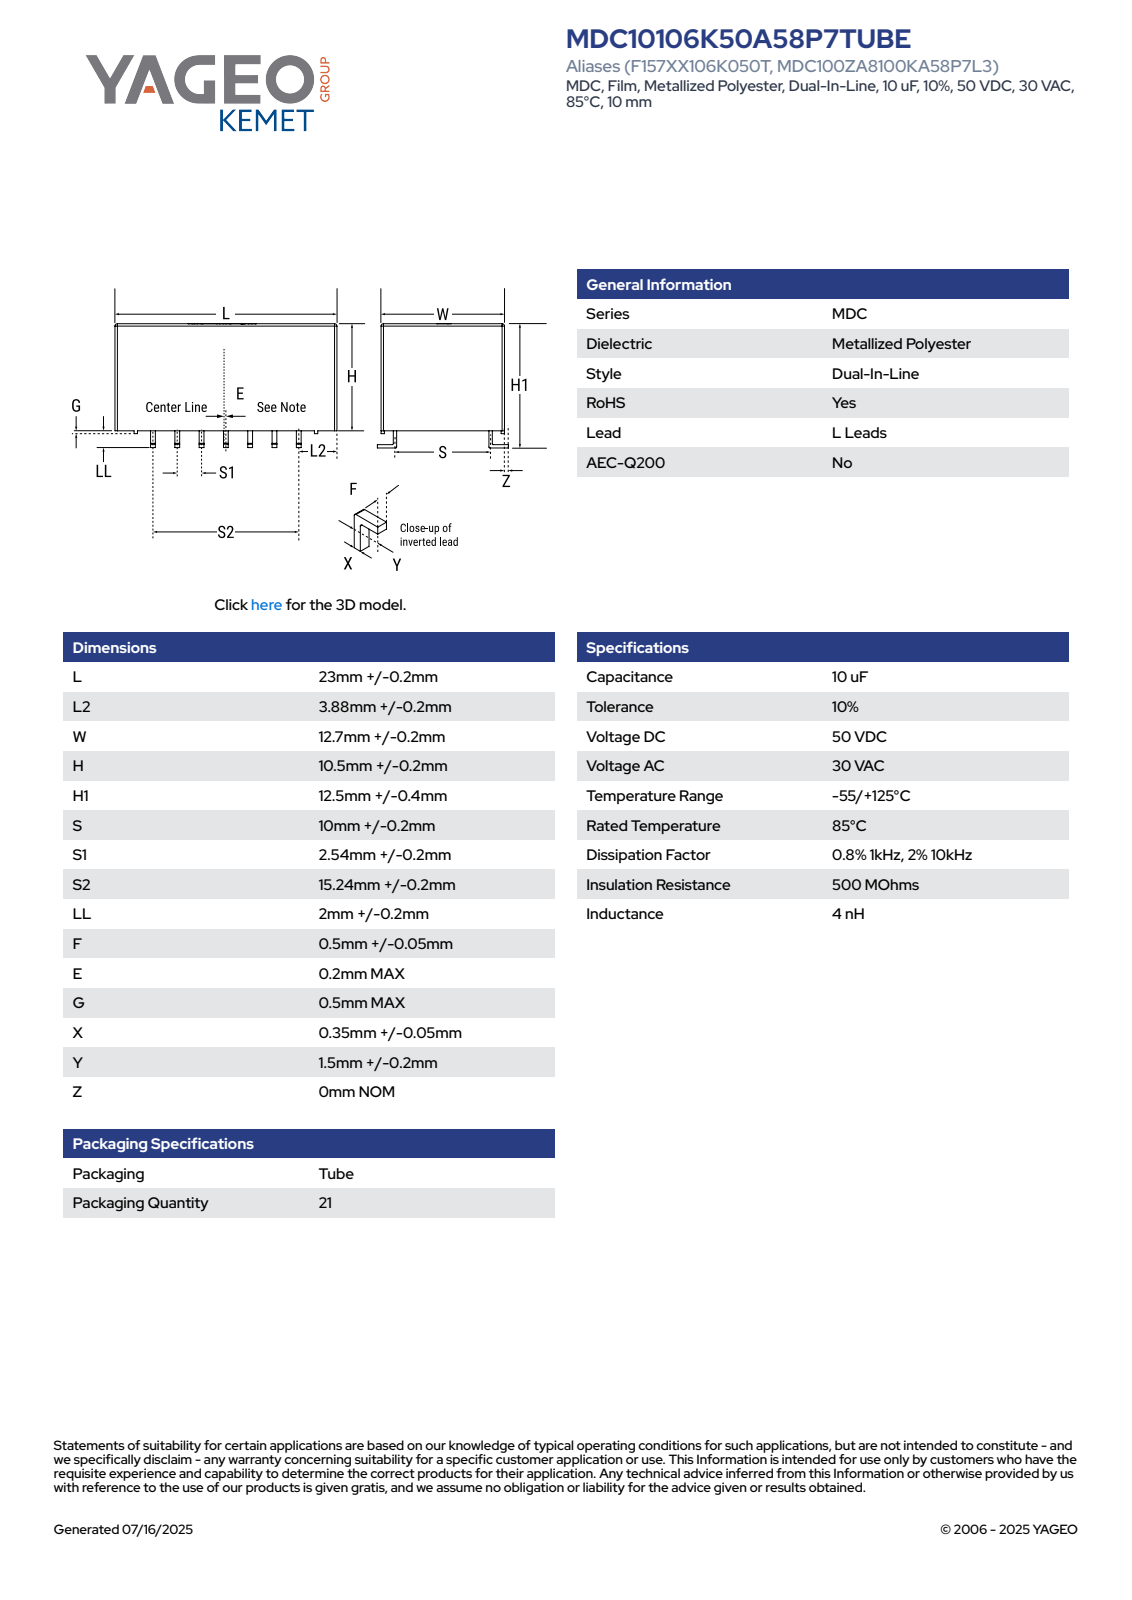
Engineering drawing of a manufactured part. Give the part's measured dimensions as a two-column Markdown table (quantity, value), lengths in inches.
| quantity | value |
| --- | --- |
| part name | CFS_KD14MDC_A58_L23.2L24.08W12.9H10.7S10LL2.2 |
| STEP written by | SolidWorks 2021 (AUTOMOTIVE_DESIGN) |
| units | inches |
| bodies | 4 solids, 173 faces (169 planar, 0 cylindrical, 4 other) |
| overall size | 0.913 × 0.52 × 0.508 |
| volume | 0.196 in³ |
| surface area | 2.254 in² |
| main face-to-face distances | 0.508, 0.421, 0.913, 0.016, 0.061, 0.447, 0.022, 0.1, 0.045, 0.463 |
